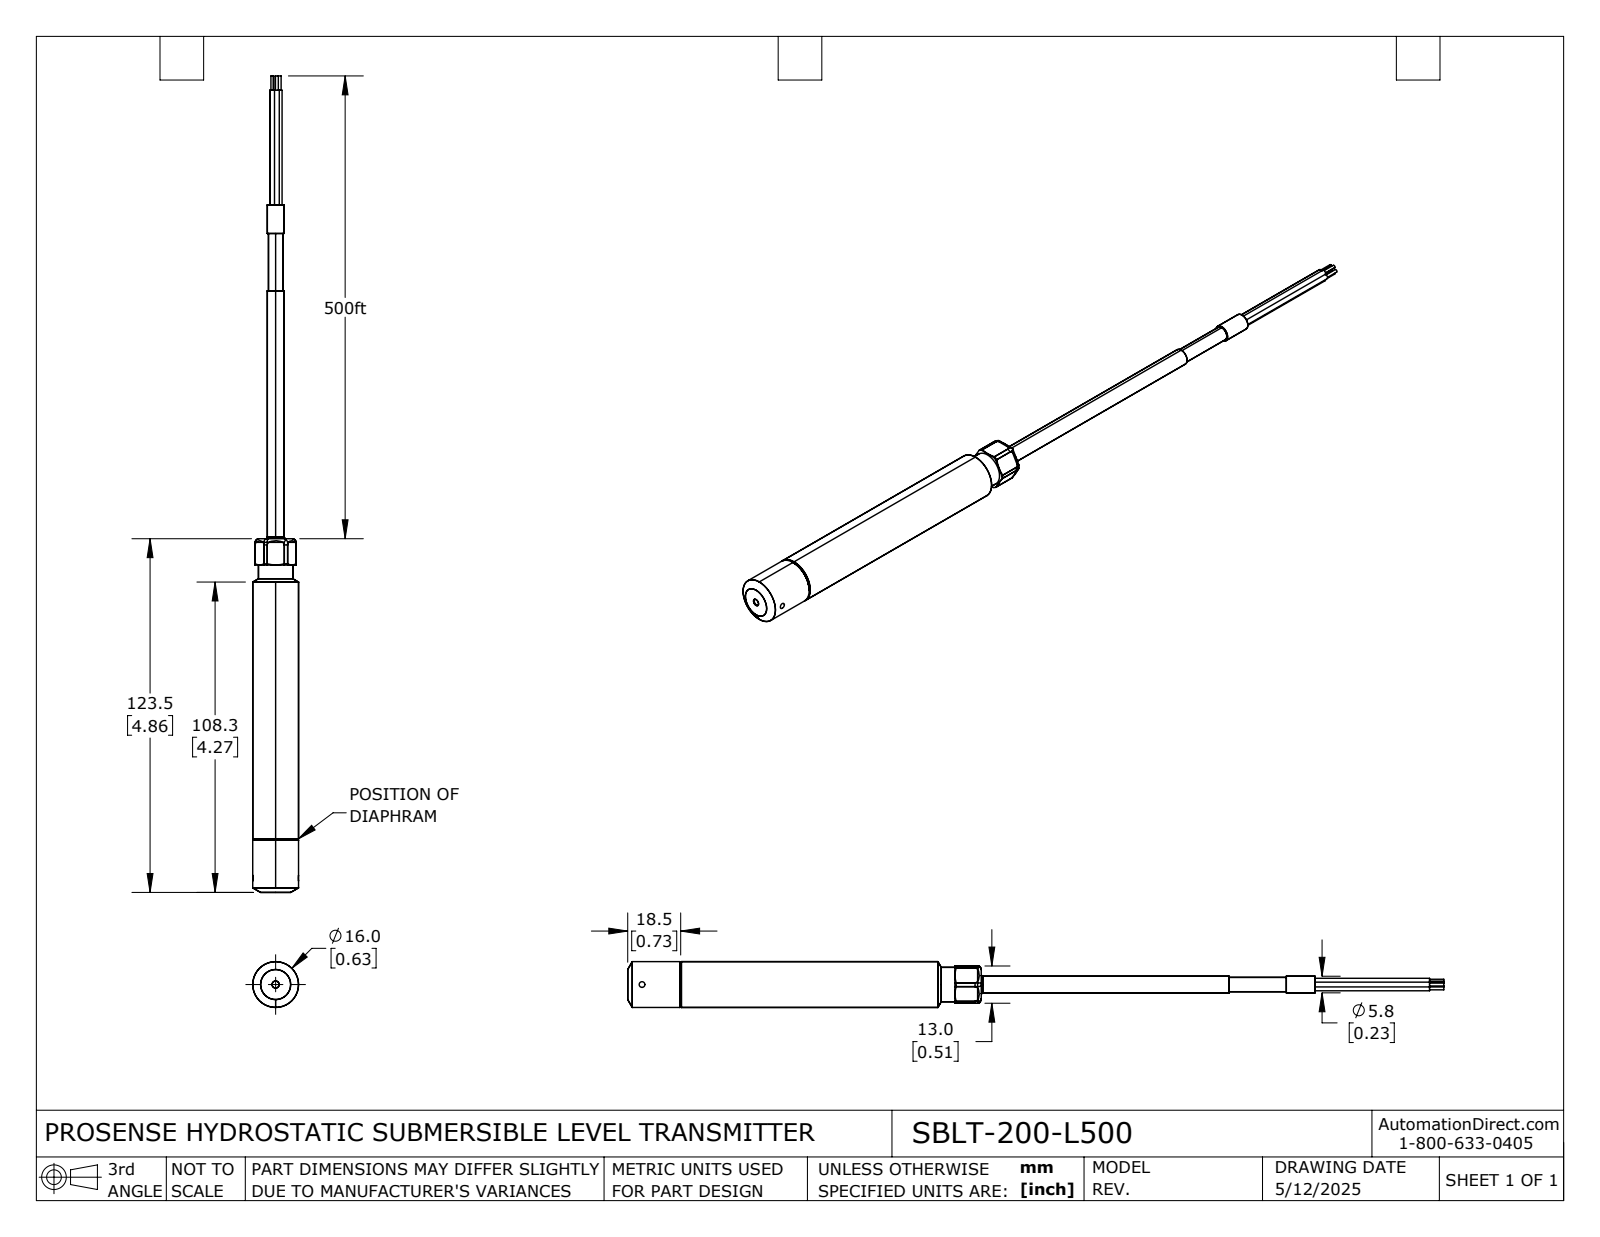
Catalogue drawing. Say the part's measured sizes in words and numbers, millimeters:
The part is named "SBLT-200-L500". Its 3-D file was written by "SolidWorks 2024 (AUTOMOTIVE_DESIGN)". It is 11 solids with 201 faces: 52 planar, 88 cylindrical and 61 other. Overall it measures 285 by 16 by 16 millimeters. Its volume is 52 410 cubic millimeters and its surface area 19 320 square millimeters. Round holes: 1 of diameter 2, 1 of diameter 2.5, 1 of diameter 9.5, 1 of diameter 13.1, 1 of diameter 14. Round bosses or shafts: 5 of diameter 1.7, 5 of diameter 1, 1 of diameter 16, 1 of diameter 16, 1 of diameter 12, 1 of diameter 12, 1 of diameter 6.2, 1 of diameter 5.8. Partial cylindrical surfaces (rounded edges, fillets, slot ends): 6 of radius 1.3, 1 of radius 7.1. The main face-to-face distances are 13, 123.5, 110, 13.5, 116.6, 226.5, 240, 95.8, 5, 221.5.
